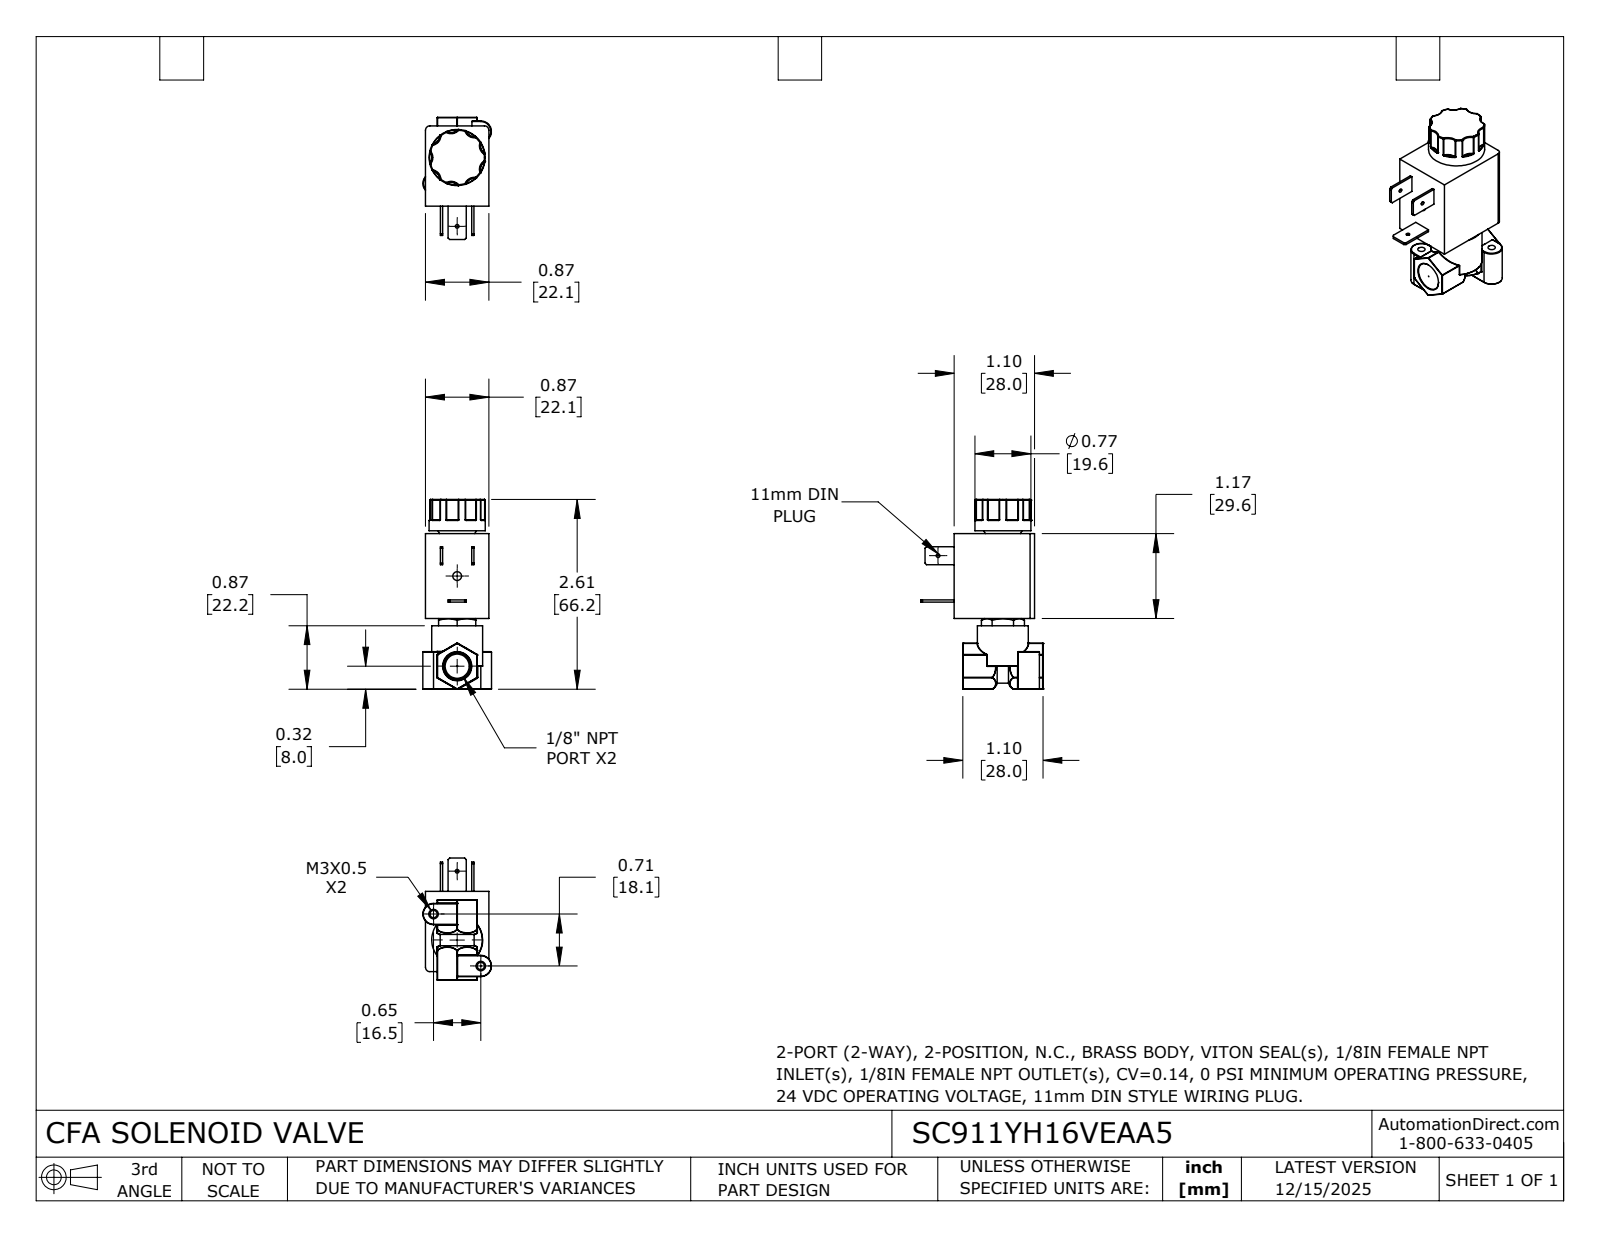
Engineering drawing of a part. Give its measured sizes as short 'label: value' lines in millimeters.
name: SC911YH16VEAA5
written by: SolidWorks 2024 (CONFIG_CONTROL_DESIGN)
unit: mm
bodies: 1 solid, 393 faces (76 planar, 108 cylindrical, 209 other)
size: 66.2 × 42.6 × 23.9
volume: 28 070 mm³; area: 9 271 mm²
holes: 2× ⌀1.3, 2× ⌀2.5, 1× ⌀3
bosses: 1× ⌀19.6, 1× ⌀17.8, 1× ⌀8.4
rounds: 27× R0.1, 18× R0.3, 12× R0.2, 7× R3.4, 2× R0.4, 2× R1.5, 2× R3.4, 2× R3.7
face distances: 22.1, 28, 29.6, 41.6, 11.9, 13.9, 4.1, 18, 30.7, 1
hole spacings: 17.1, 24.5, 34.1
